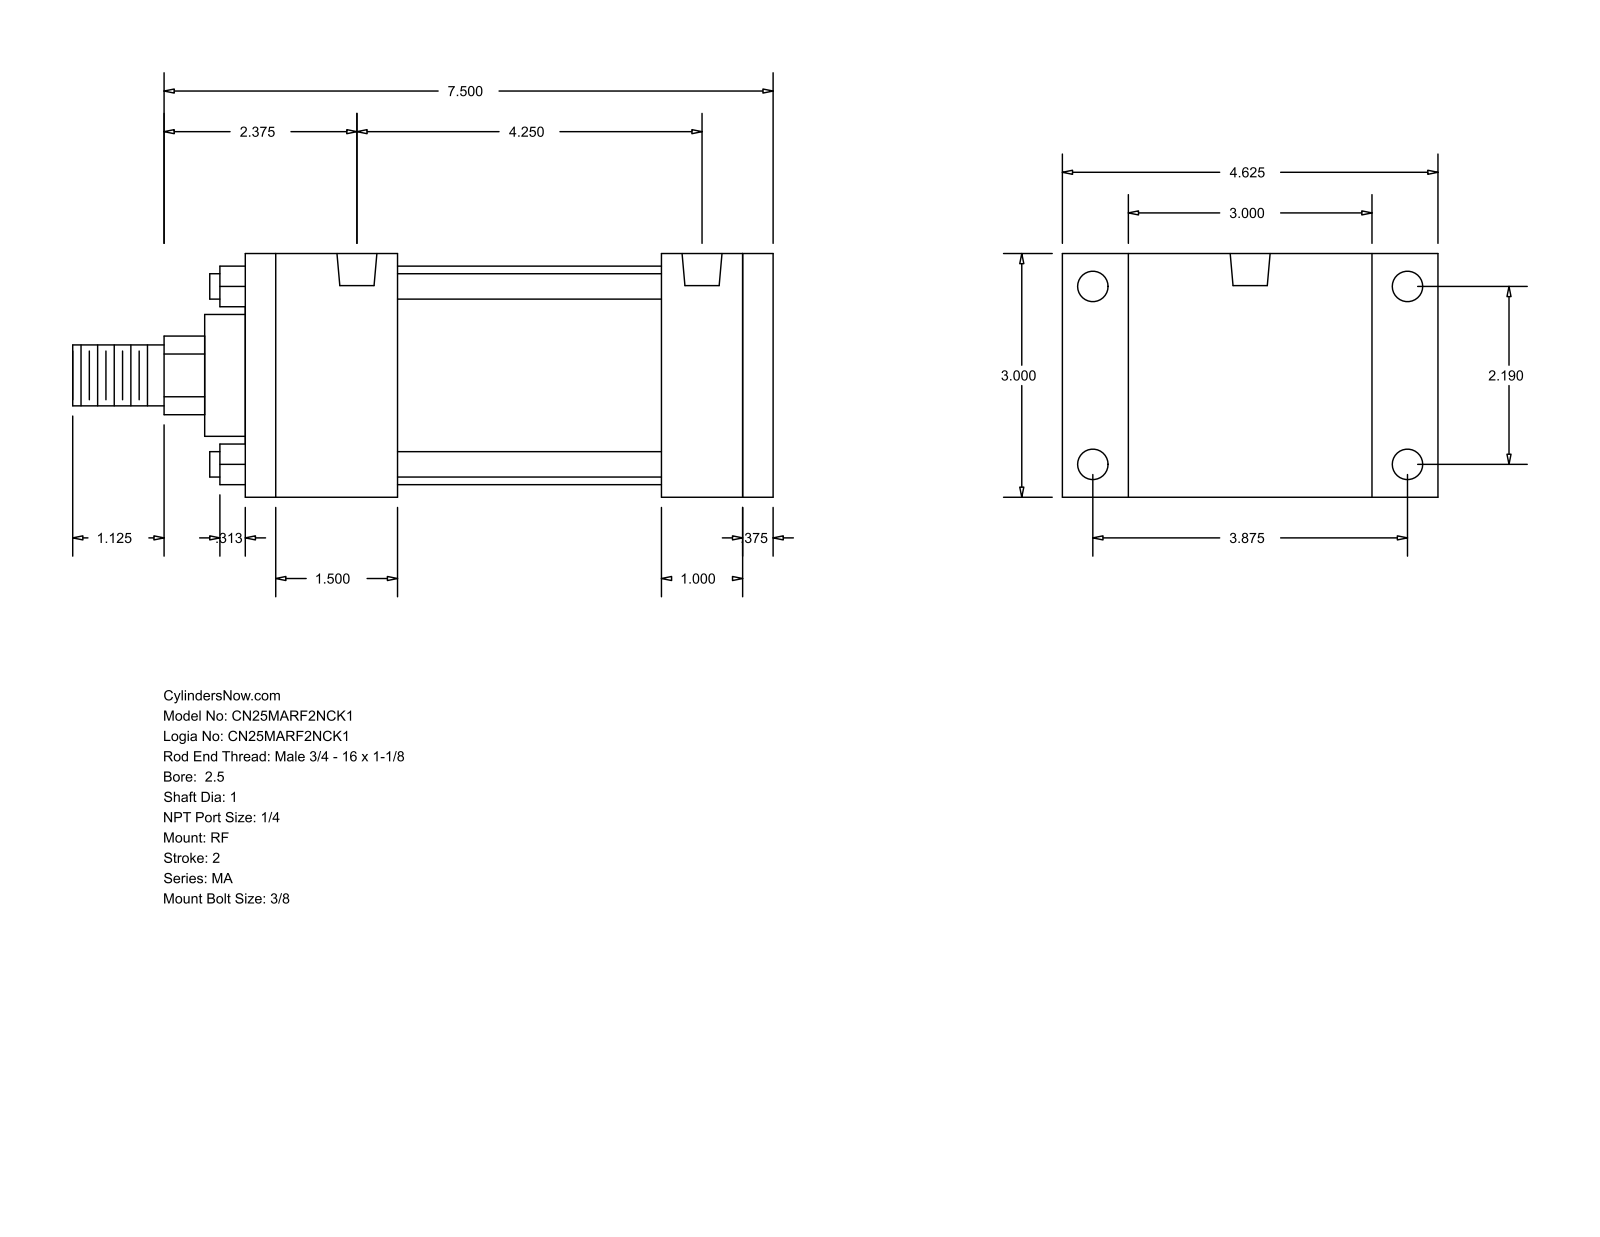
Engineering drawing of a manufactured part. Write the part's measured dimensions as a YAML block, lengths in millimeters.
part_name: "MA_RF__0250_1"
step_written_by: "GSSL Pune (CONFIG_CONTROL_DESIGN)"
units: millimeters
bodies: {solids: 0, faces: 92, planar: 64, cylindrical: 28, other: 0}
overall_size: [219.07, 117.47, 76.2]
round_holes:
  - {diameter: 7.94, count: 4}
  - {diameter: 9.53, count: 4}
  - {diameter: 12.49, count: 2}
round_bosses_or_shafts:
  - {diameter: 7.94, count: 4}
  - {diameter: 68.33, count: 1}
  - {diameter: 38.1, count: 1}
  - {diameter: 25.4, count: 1}
  - {diameter: 19.05, count: 1}
partial_cylinders:
  - {radius: 12.29, count: 1}
face_to_face_distances: [76.2, 165.1, 155.57, 9.53, 25.4, 47.63, 130.17, 82.54, 107.94, 117.47]
hole_center_spacings: [55.62, 98.42, 107.95, 113.05]
